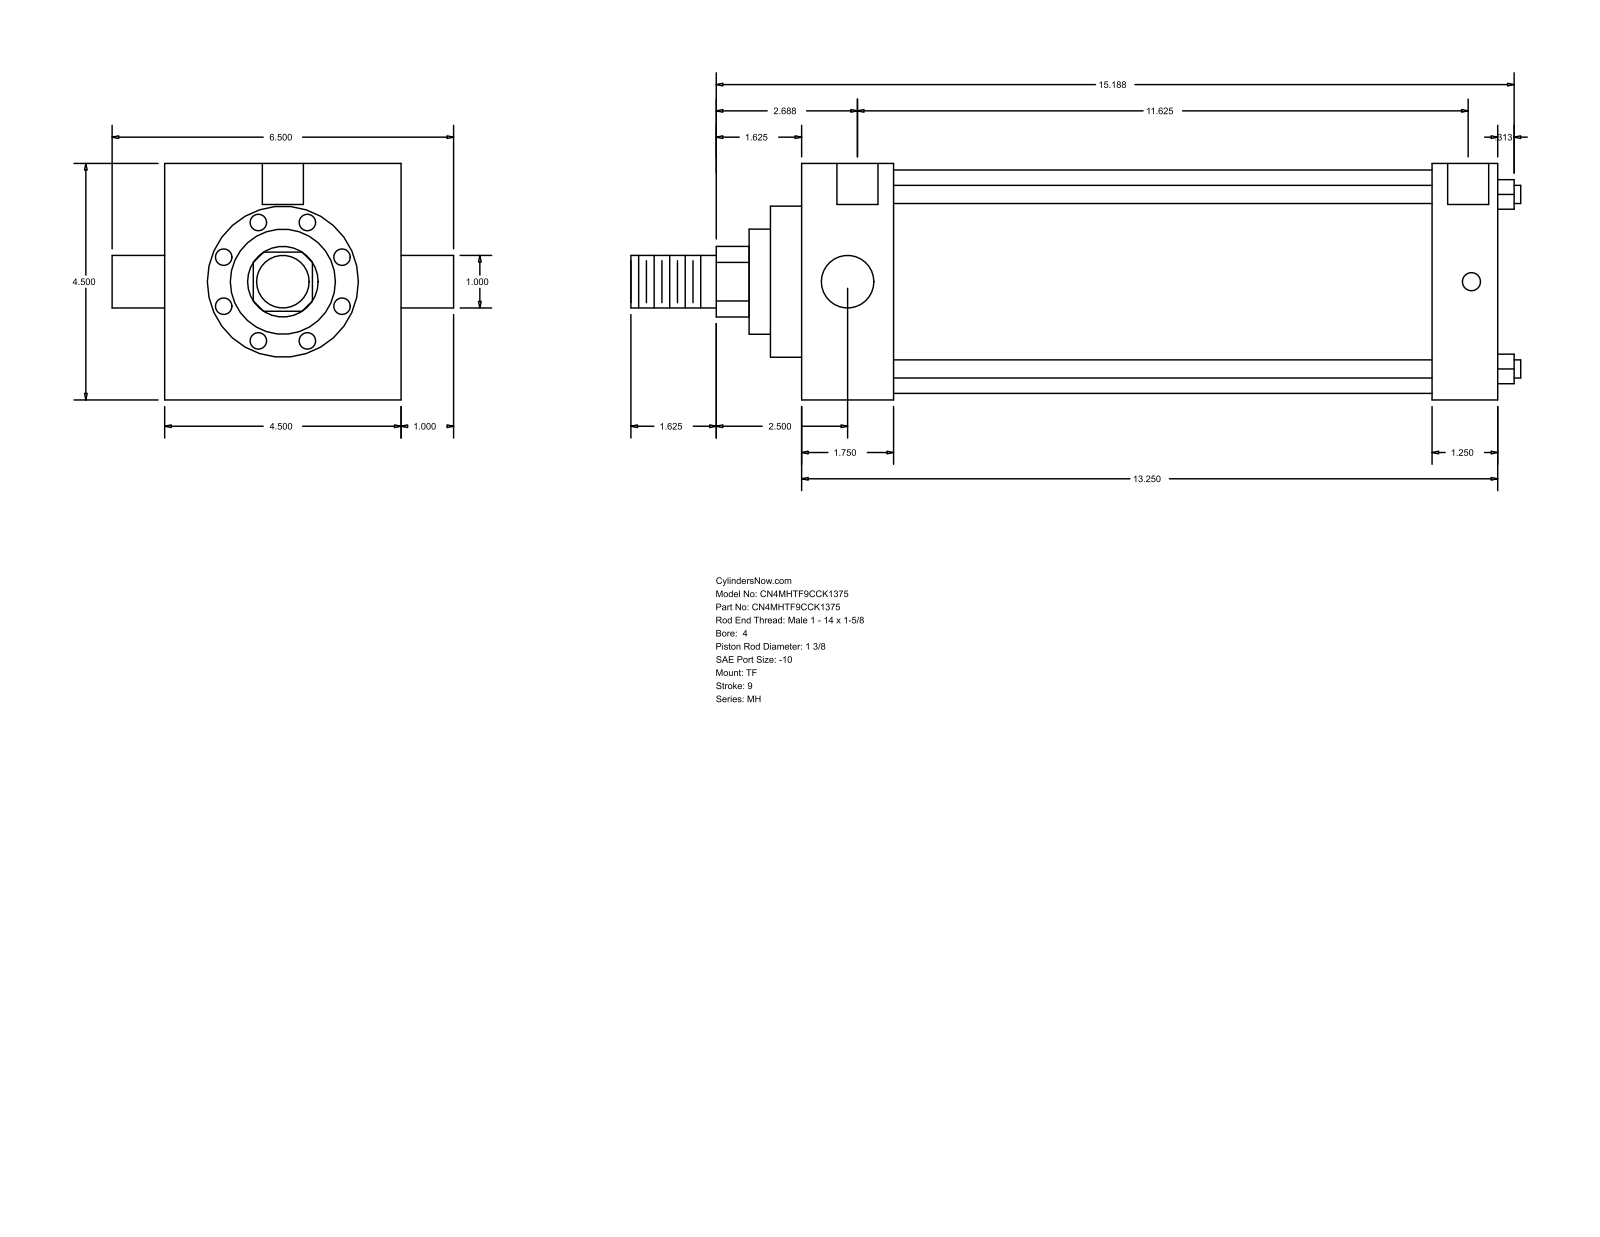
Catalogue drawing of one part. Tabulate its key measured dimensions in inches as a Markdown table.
| quantity | value |
| --- | --- |
| part name | MH_TF__0400_1.375 |
| STEP written by | GSSL Pune (CONFIG_CONTROL_DESIGN) |
| units | inches |
| bodies | 0 solids, 86 faces (61 planar, 25 cylindrical, 0 other) |
| overall size | 16.937 × 6.5 × 4.5 |
| round holes (diameter × count) | 0.344 × 3, 0.781 × 2 |
| round bosses / shafts (diameter × count) | 0.345 × 4, 1 × 2, 4.25 × 1, 2.875 × 1, 2 × 1, 1.375 × 1 |
| partial cylindrical surfaces (radius × count) | 0.672 × 1 |
| main face-to-face distances | 4.5, 13.25, 1.75, 11.5, 12, 10.25, 1.25, 0.594, 2.344, 12.594 |
| hole center spacings | 0.062, 0.063, 11.625, 11.687, 11.688, 11.75 |
